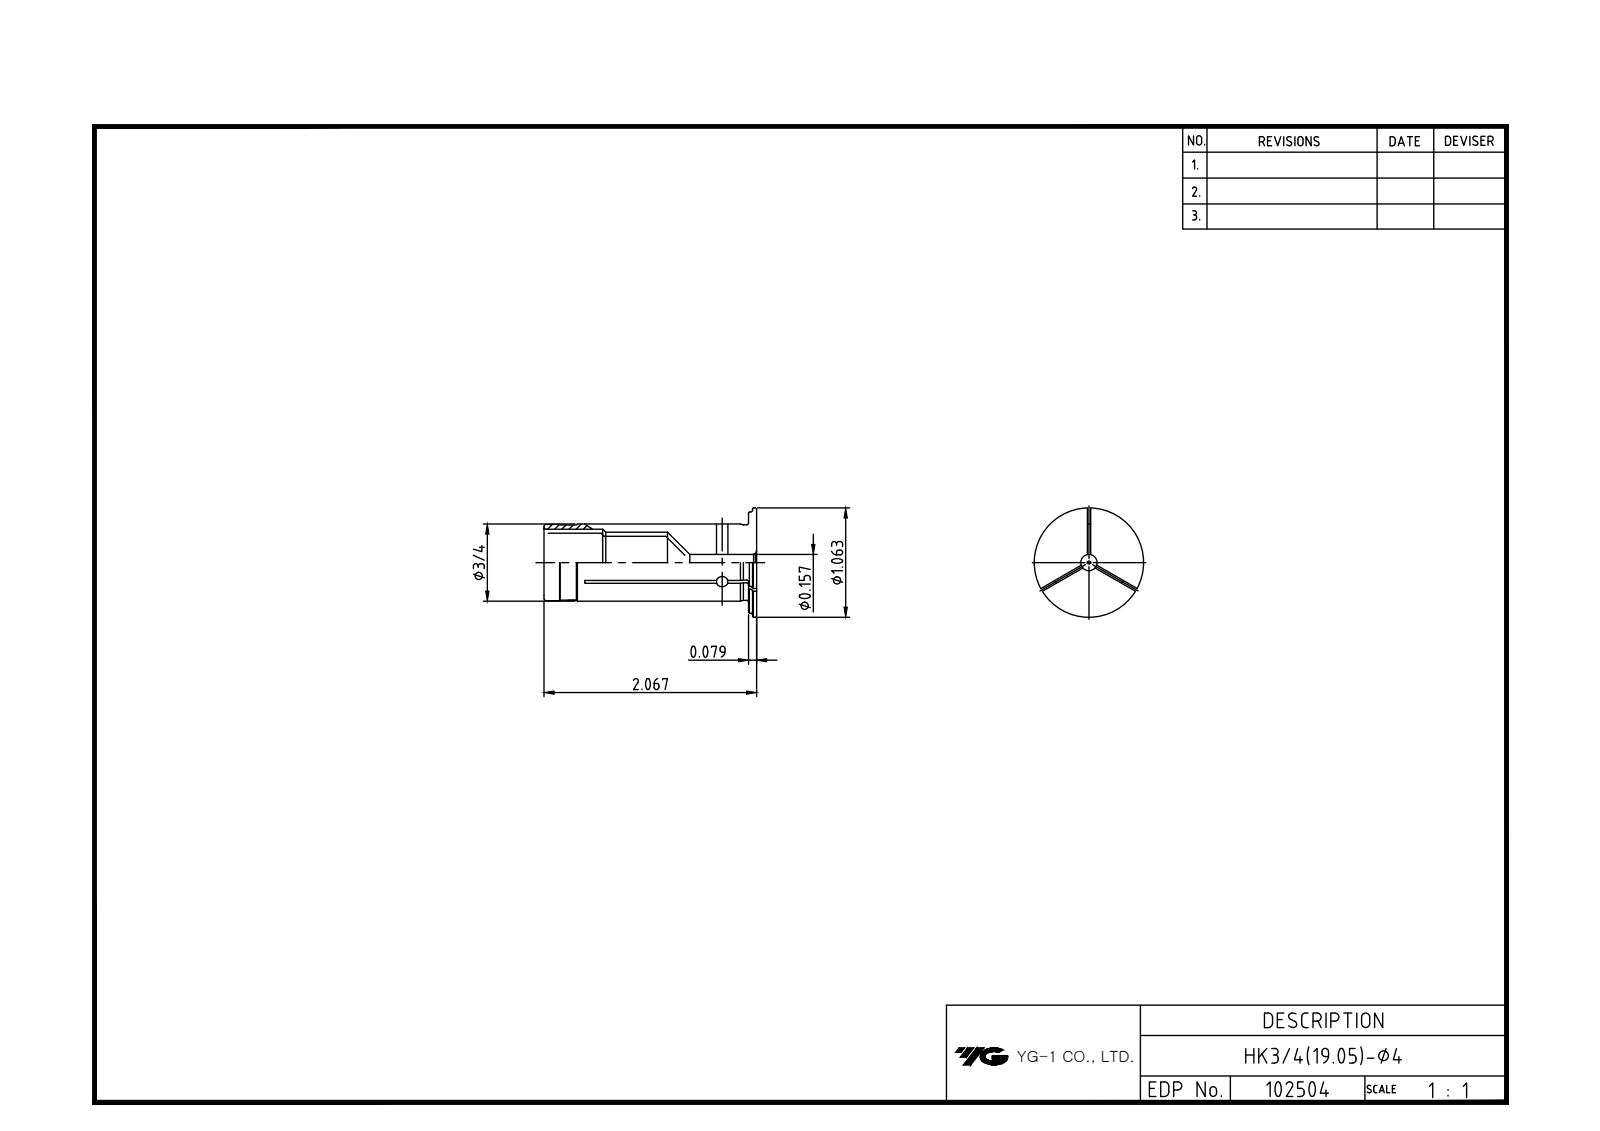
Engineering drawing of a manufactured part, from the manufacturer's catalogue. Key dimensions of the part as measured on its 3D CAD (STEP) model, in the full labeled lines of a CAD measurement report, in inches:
Part name (STEP PRODUCT): LO-HK19.05-4
STEP written by: Autodesk Inventor 2025 (AP242_MANAGED_MODEL_BASED_3D_ENGINEERING_MIM_LF)
Units: inches
Bodies: 1 solid, 12 faces (4 planar, 6 cylindrical, 2 other)
Overall size (bounding box): 2.067 × 1.063 × 1.063
Volume: 0.542 in³ · Surface area: 9.404 in²
Round holes (diameter × count): ⌀0.157 ×1, ⌀0.591 ×1, ⌀0.65 ×1
Round bosses / shafts (diameter × count): ⌀1.063 ×1, ⌀0.984 ×1, ⌀0.75 ×1
Main face-to-face distances: 0.079, 0.039, 1.988, 2.028, 2.067
